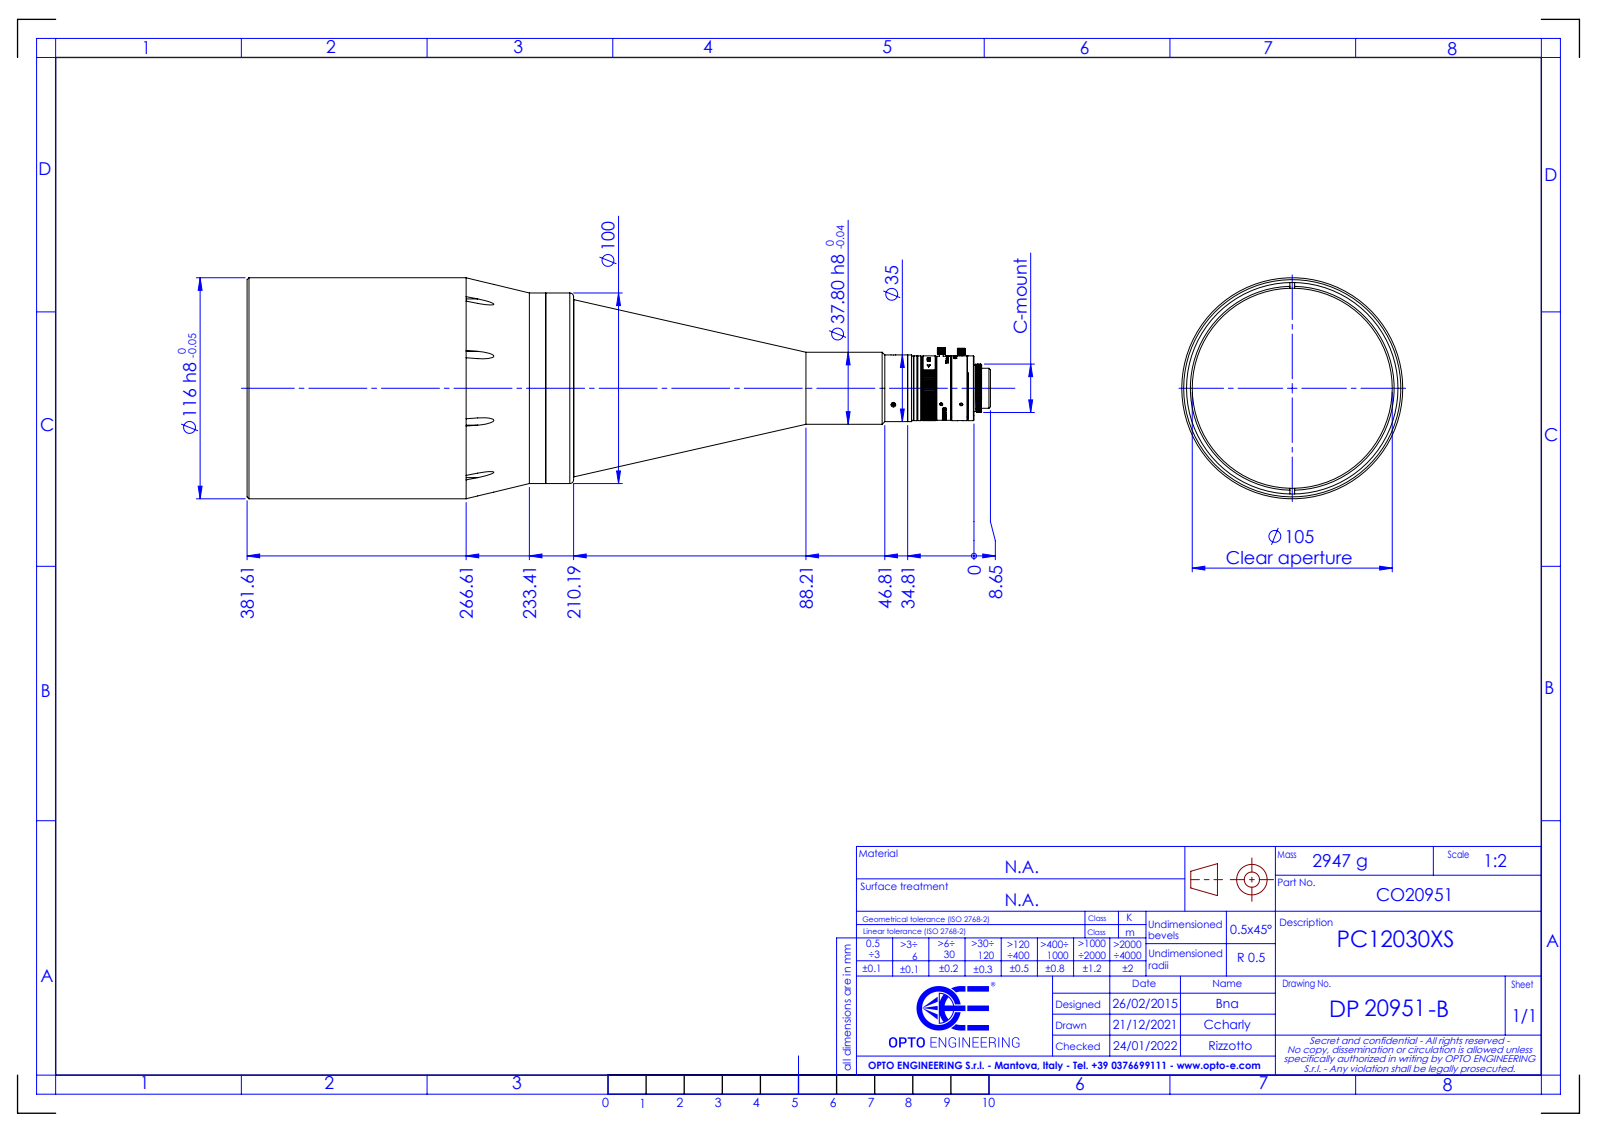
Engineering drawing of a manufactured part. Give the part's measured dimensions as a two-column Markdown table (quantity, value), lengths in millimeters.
| quantity | value |
| --- | --- |
| part name | DP20951-B_PC12030XS |
| STEP written by | SolidWorks 2021 (CONFIG_CONTROL_DESIGN) |
| units | millimeters |
| bodies | 0 solids, 609 faces (242 planar, 200 cylindrical, 167 other) |
| overall size | 390.26 × 116 × 116 |
| round holes (diameter × count) | 1.4 × 4, 2.5 × 3, 2 × 1, 2.6 × 1, 21.4 × 1, 23.2 × 1, 31.08 × 1, 32.6 × 1, 105 × 1, 111 × 1 |
| round bosses / shafts (diameter × count) | 116 × 1, 100 × 1, 93 × 1, 37.8 × 1, 35 × 1, 34 × 1, 33.8 × 1, 33.6 × 1 |
| partial cylindrical surfaces (radius × count) | 2 × 12, 16.7 × 1, 16.88 × 1, 17.08 × 1, 17.09 × 1 |
| main face-to-face distances | 150.3, 6, 156.3, 0.5, 6.5, 156.8, 171.42, 170.92, 164.92, 14.62 |
| hole center spacings | 10.51, 25.13, 35.64, 35.08 |
